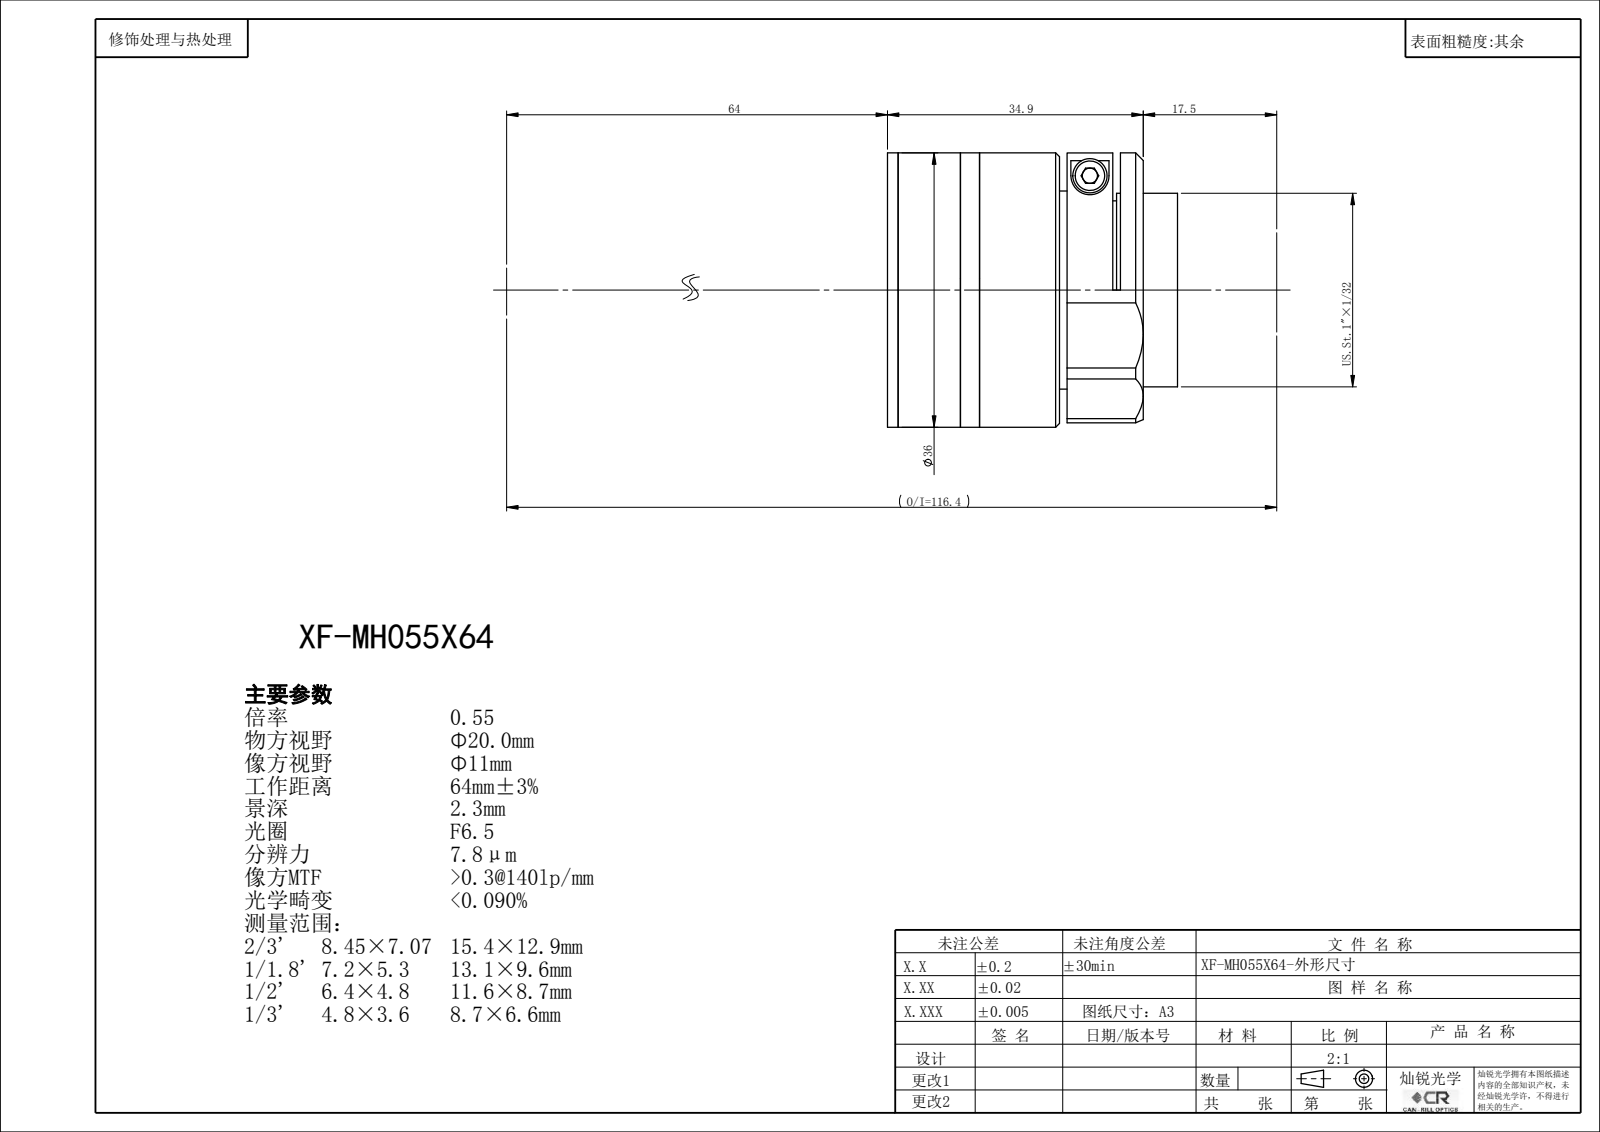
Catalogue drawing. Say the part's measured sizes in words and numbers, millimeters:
The part is named "XF-MH055X64". Its 3-D file was written by "SolidWorks 2014 (CONFIG_CONTROL_DESIGN)". It is 3 solids with 161 faces: 59 planar, 81 cylindrical and 21 other. Overall it measures 38.09 by 36 by 36 millimeters. Its volume is 25 415 cubic millimeters and its surface area 15 487 square millimeters. Round holes: 2 of diameter 2, 1 of diameter 2.05, 1 of diameter 3, 1 of diameter 8, 1 of diameter 10.4, 1 of diameter 13, 1 of diameter 17, 1 of diameter 21, 1 of diameter 23, 1 of diameter 24, 1 of diameter 24.9, 1 of diameter 26. Round bosses or shafts: 1 of diameter 36, 1 of diameter 30, 1 of diameter 28, 1 of diameter 25.4, 1 of diameter 23.4, 1 of diameter 20, 1 of diameter 4.5, 1 of diameter 2.5. Partial cylindrical surfaces (rounded edges, fillets, slot ends): 5 of radius 25, 1 of radius 2.5. The main face-to-face distances are 3, 14.28, 2, 1, 2.28, 17.28, 34.87, 10, 24.87, 7. The hole center spacings are 12, 24.
